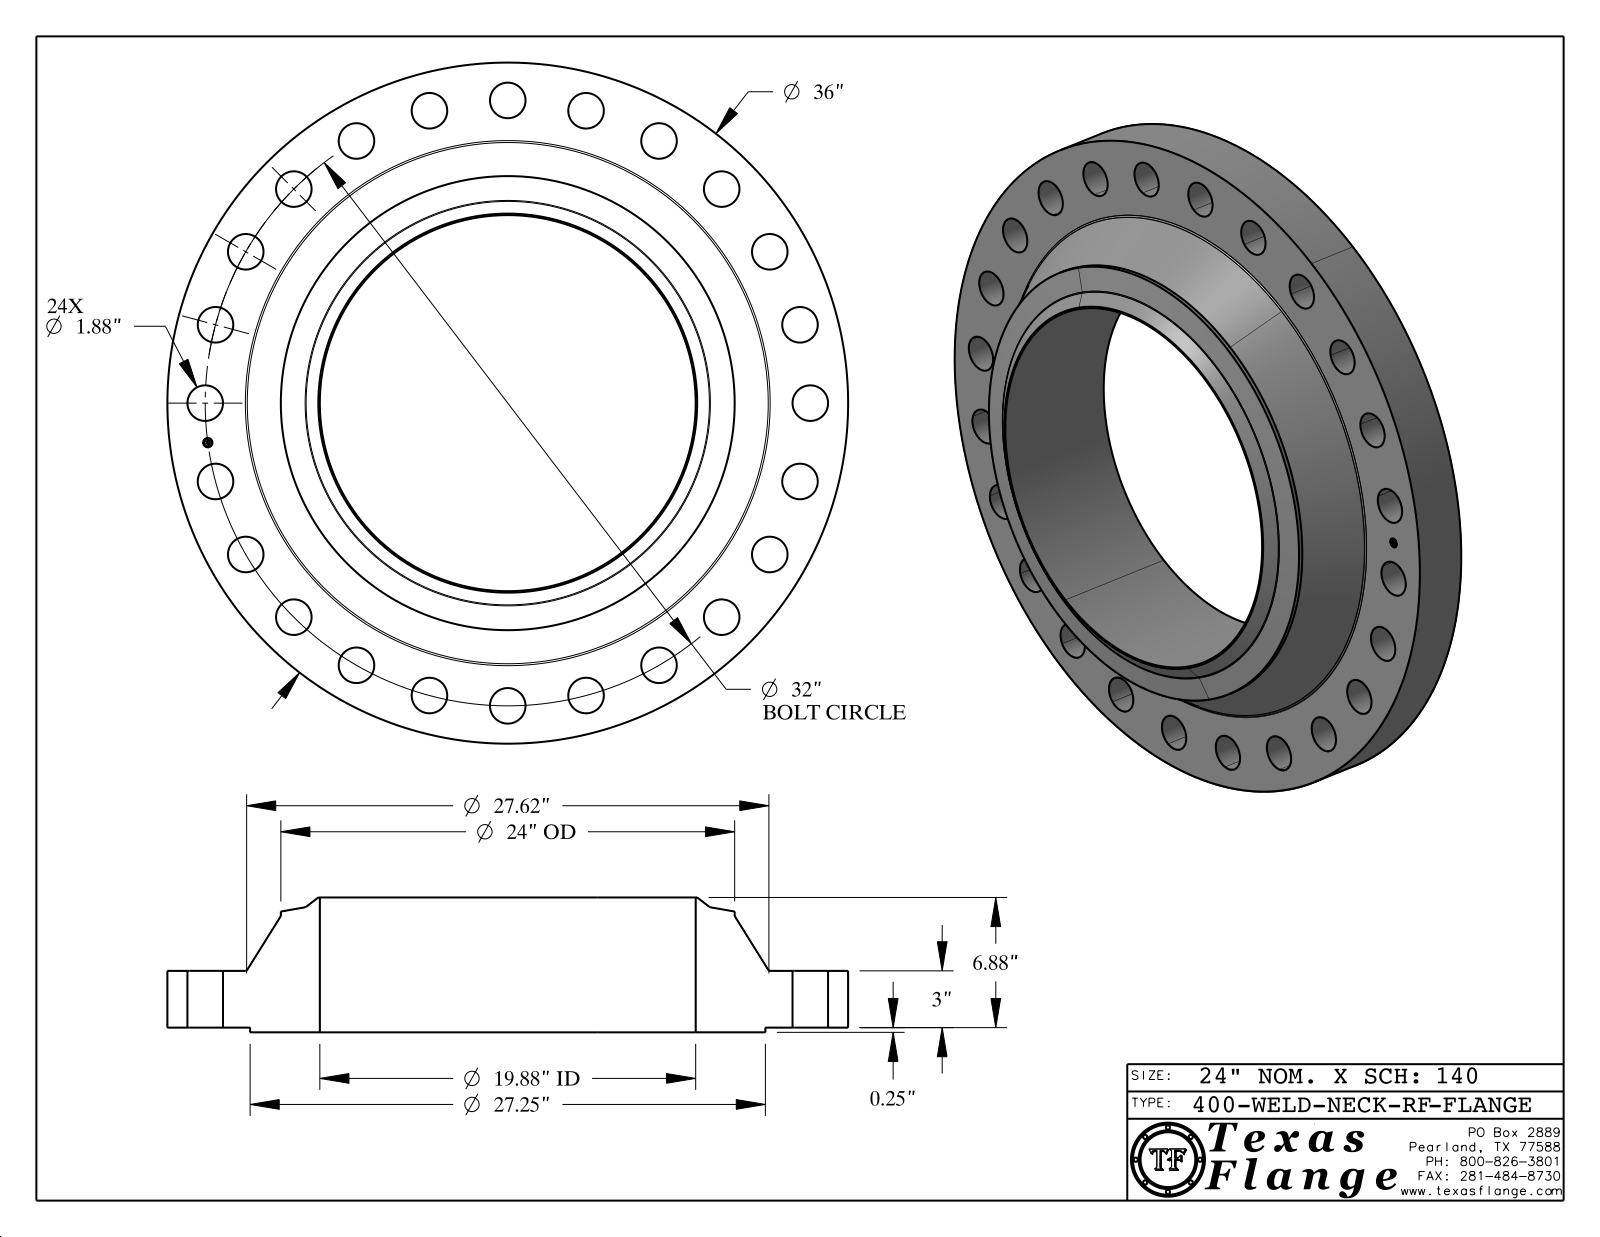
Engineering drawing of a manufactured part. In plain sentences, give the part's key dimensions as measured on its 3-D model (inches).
The part is named "400-WELD-NECK-RF". Its 3-D file was written by "CATIA V5 STEP AP214 (AUTOMOTIVE_DESIGN)". It is 1 solid with 455 faces: 369 planar, 76 cylindrical and 10 other. Overall it measures 36 by 36 by 7.13 inches. Its volume is 2 680 cubic inches and its surface area 2 673 square inches. Round holes: 24 of diameter 1.88, 1 of diameter 0.495, 1 of diameter 19.876. Round bosses or shafts: 8 of diameter 0.03, 1 of diameter 36, 1 of diameter 27.25, 1 of diameter 24, 1 of diameter 0.39. The main face-to-face distances are 3, 0.25, 3.25, 7.13, 6.88, 3.88, 3.235, 2.985, 0.015, 3.895. The hole center spacings are 16, 30.909, 4.177, 8.282, 12.246, 19.48, 22.627, 25.387.
